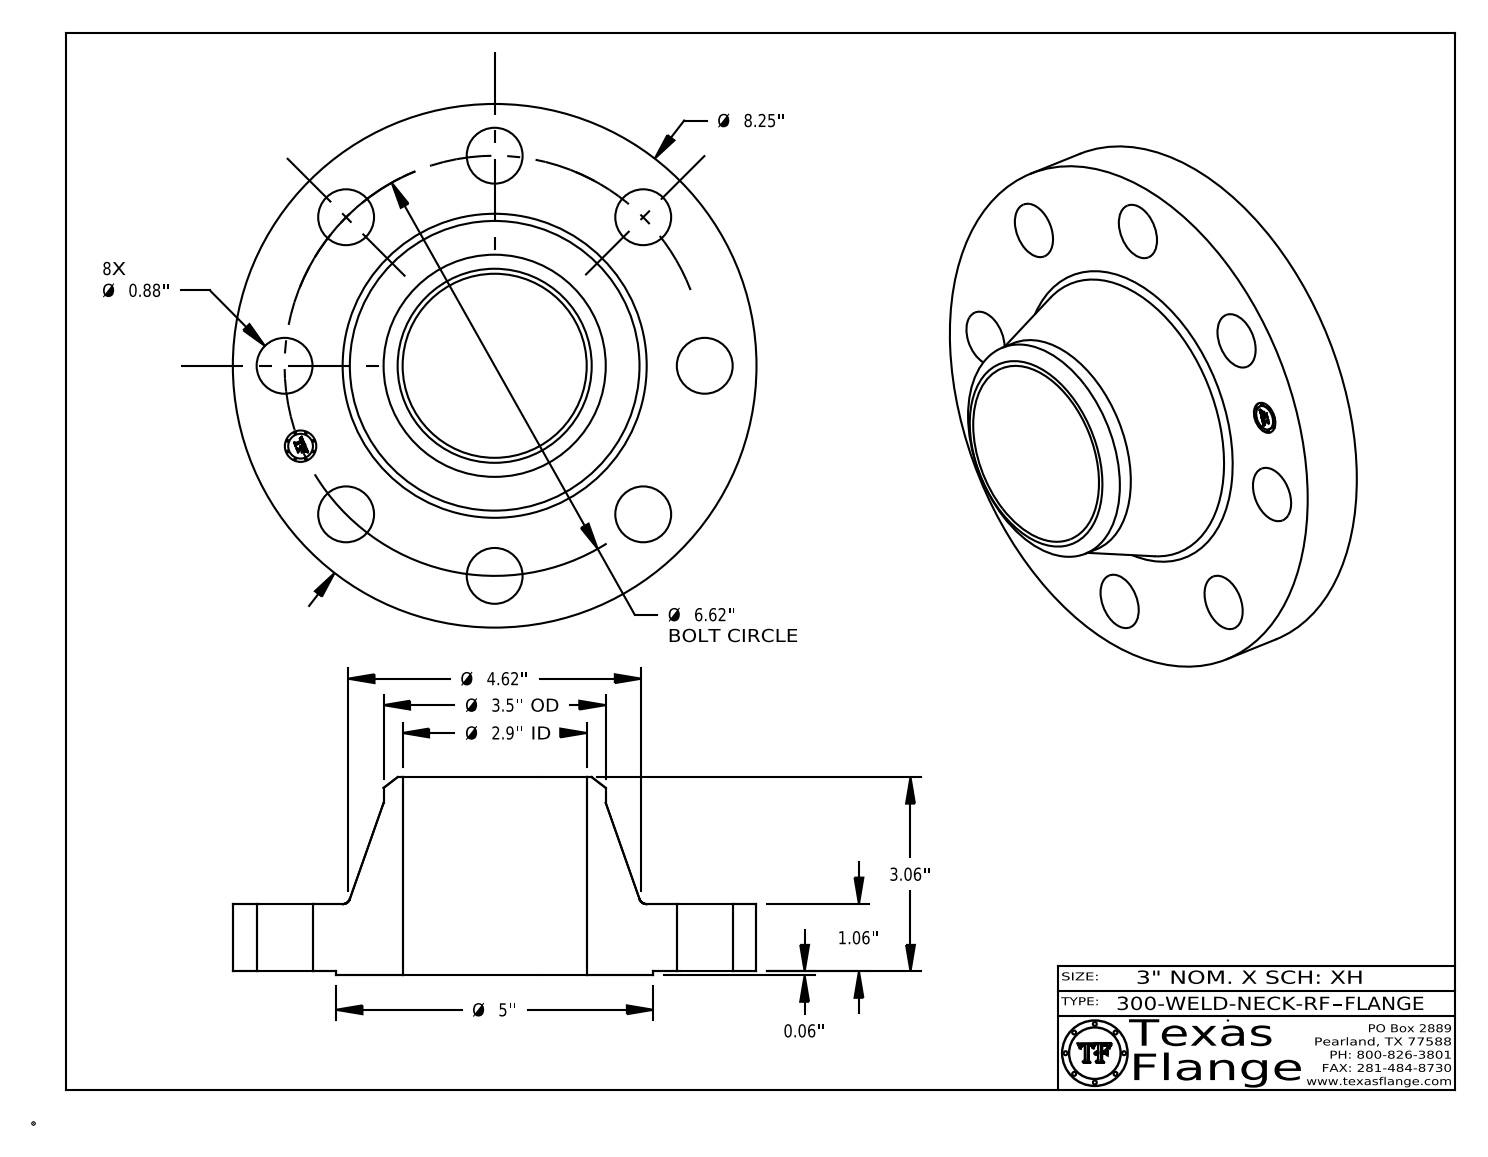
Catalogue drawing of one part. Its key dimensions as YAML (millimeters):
part_name: "300-WELD-NECK-RF"
step_written_by: "CATIA V5 STEP AP214 (AUTOMOTIVE_DESIGN)"
units: millimeters
bodies: {solids: 1, faces: 419, planar: 369, cylindrical: 44, other: 6}
overall_size: [209.6, 209.6, 79.3]
volume: 927500
surface_area: 117200
round_holes:
  - {diameter: 22.4, count: 8}
  - {diameter: 12.6, count: 1}
  - {diameter: 73.7, count: 1}
round_bosses_or_shafts:
  - {diameter: 0.8, count: 8}
  - {diameter: 209.6, count: 1}
  - {diameter: 127, count: 1}
  - {diameter: 88.9, count: 1}
  - {diameter: 9.9, count: 1}
face_to_face_distances: [26.9, 1.6, 28.5, 79.3, 77.7, 50.8, 0.4, 28.1, 26.5, 51.2]
hole_center_spacings: [84.1, 64.3, 155.3, 118.9, 118.9, 32.8, 93.4, 164.9]
